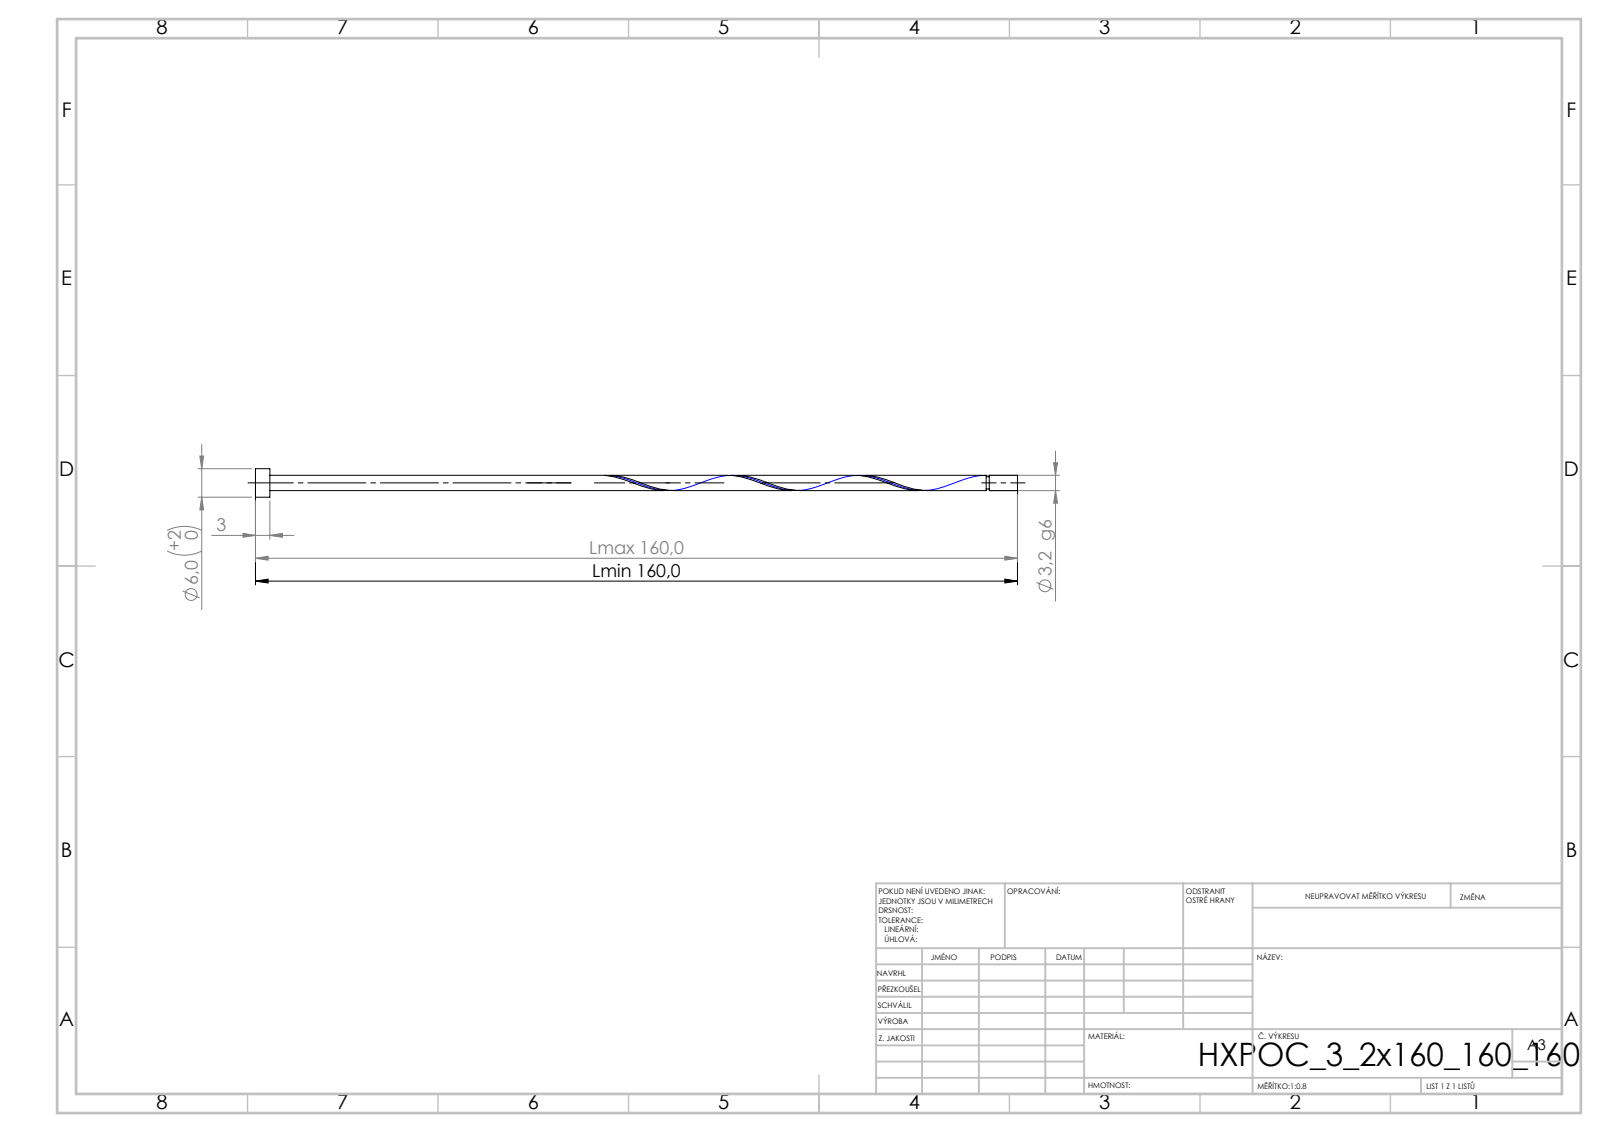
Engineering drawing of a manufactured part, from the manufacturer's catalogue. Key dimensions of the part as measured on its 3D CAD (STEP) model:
STEP written by: SolidWorks 2019 (CONFIG_CONTROL_DESIGN)
Units: millimetres
Bodies: 1 solid, 21 faces (6 planar, 14 cylindrical, 1 other)
Overall size (bounding box): 160 × 6 × 6
Volume: 1 333 mm³ · Surface area: 1 722 mm²
Round bosses / shafts (diameter × count): ⌀6 ×1, ⌀3.2 ×1, ⌀2.56 ×1
Main face-to-face distances: 3, 160, 157, 154.08, 151.08, 5.92, 153.44, 150.44, 0.64, 6.56
